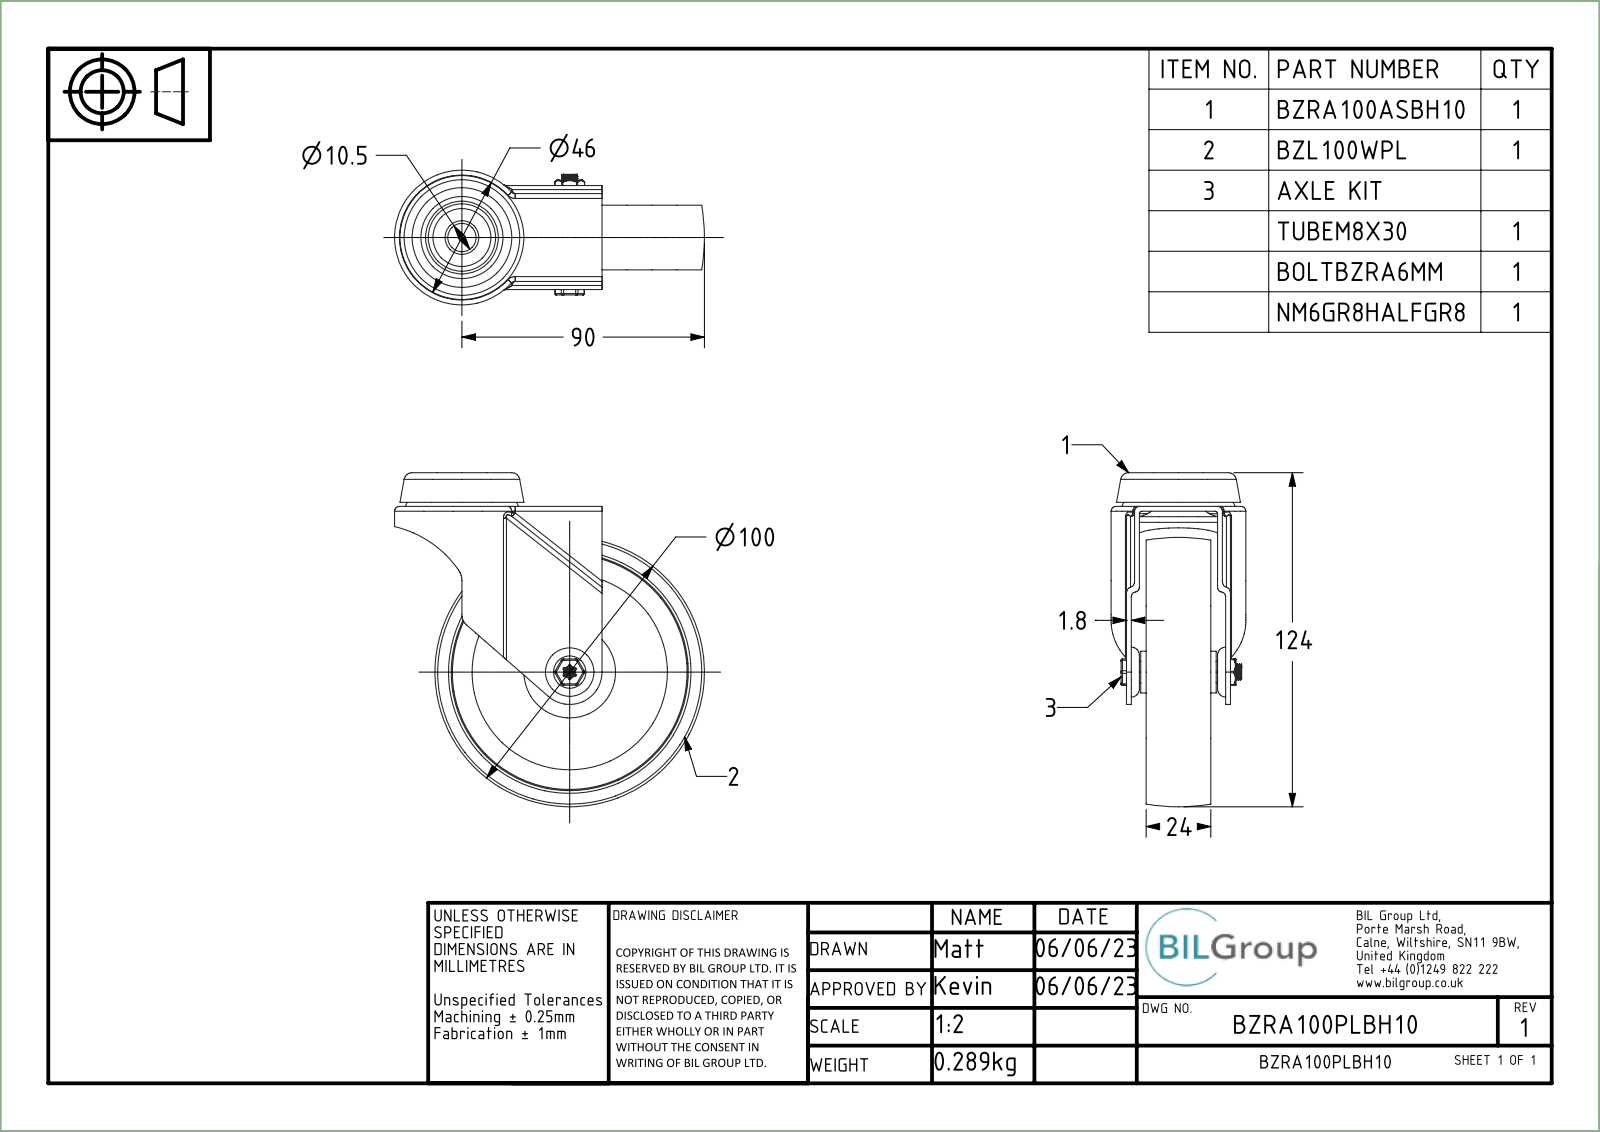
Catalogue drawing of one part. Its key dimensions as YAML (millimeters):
part_name: "BZRA100ASBH10; ZINC PLATED PRESSED STEEL HEAD; ZINC PLATED PRESSED STEEL FORKS; BZRA100PLBH10 (+8 more)"
step_written_by: "Spatial InterOp 3D (CONFIG_CONTROL_DESIGN)"
units: millimeters
bodies: {solids: 6, faces: 383, planar: 58, cylindrical: 165, other: 160}
overall_size: [124, 115, 50]
volume: 93380
surface_area: 62023
round_holes:
  - {diameter: 6, count: 1}
  - {diameter: 6.3, count: 1}
  - {diameter: 6.4, count: 1}
  - {diameter: 8.2, count: 1}
  - {diameter: 8.3, count: 1}
  - {diameter: 10.5, count: 1}
  - {diameter: 10.56, count: 1}
  - {diameter: 30, count: 1}
round_bosses_or_shafts:
  - {diameter: 39, count: 1}
  - {diameter: 18, count: 1}
  - {diameter: 15.5, count: 1}
  - {diameter: 14.76, count: 1}
  - {diameter: 8, count: 1}
  - {diameter: 7.95, count: 1}
  - {diameter: 5, count: 1}
partial_cylinders:
  - {radius: 1, count: 18}
  - {radius: 1.8, count: 18}
  - {radius: 0.5, count: 12}
  - {radius: 0.4, count: 6}
  - {radius: 0.9, count: 2}
  - {radius: 2.12, count: 1}
  - {radius: 5, count: 1}
  - {radius: 7, count: 1}
face_to_face_distances: [3, 1.8, 17.8, 16, 33.8, 20.8, 10.5, 7.3, 31.3, 13.5]
